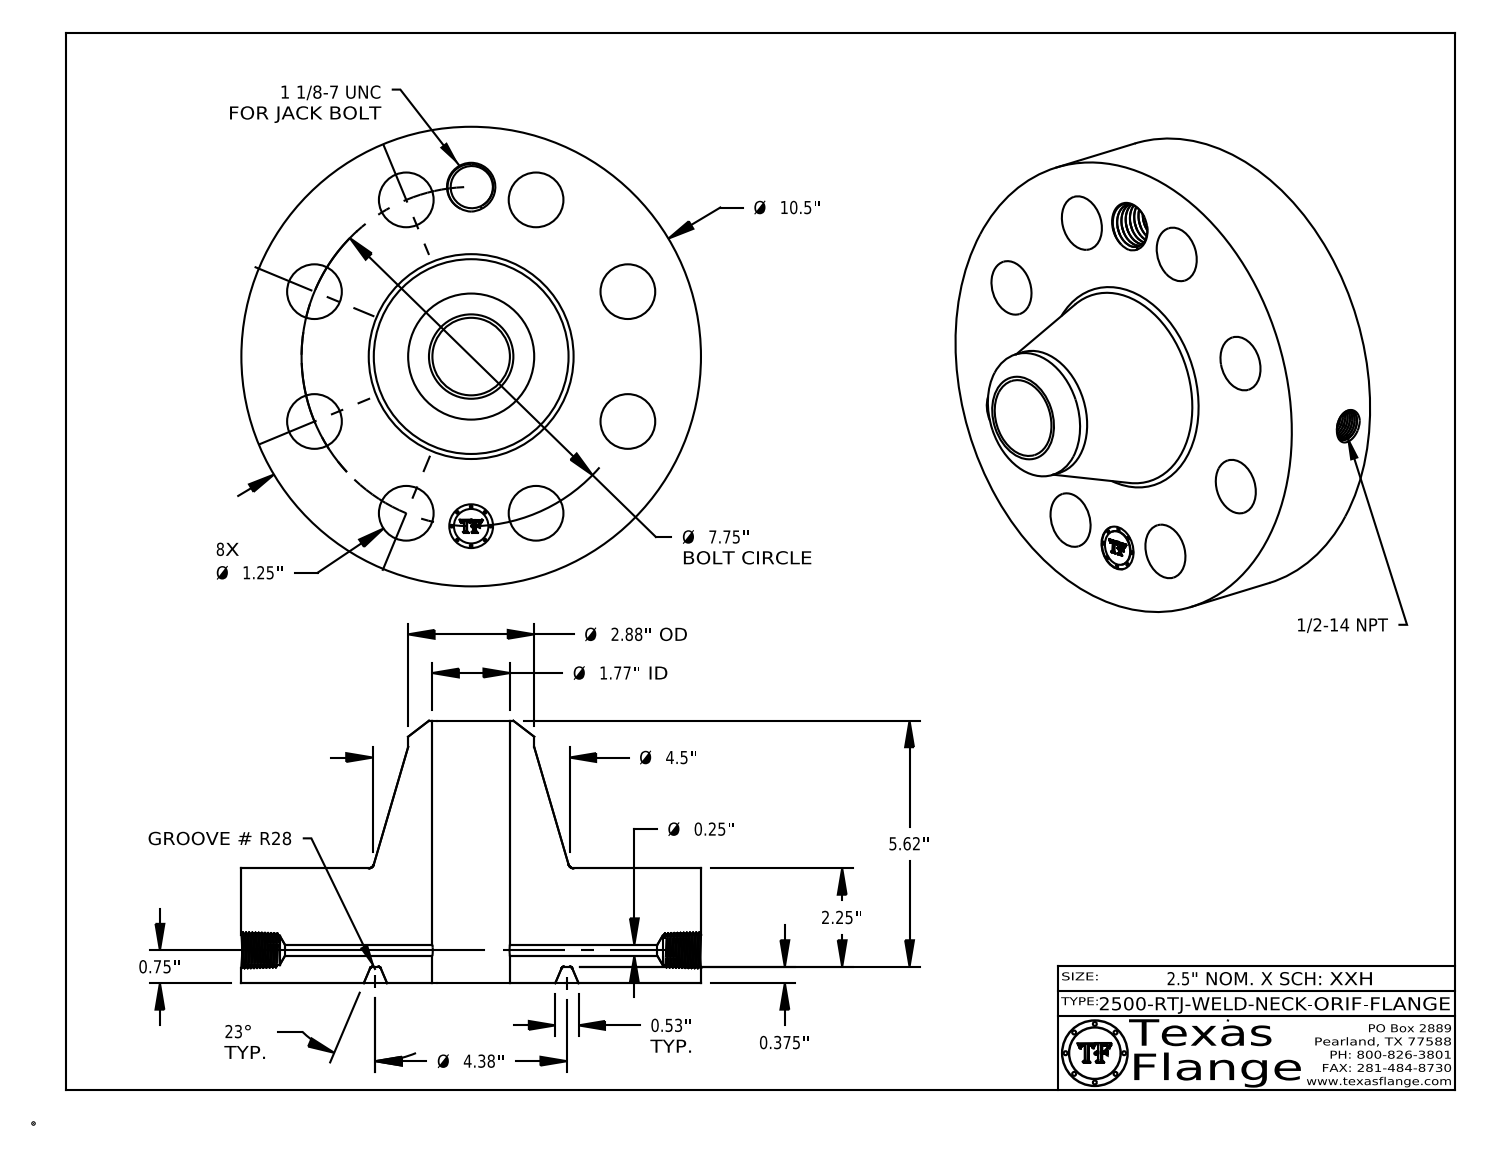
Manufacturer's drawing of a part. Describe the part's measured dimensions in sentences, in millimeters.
The part is named "2500-RTJ-WELD-NECK". Its 3-D file was written by "CATIA V5 STEP AP214 (AUTOMOTIVE_DESIGN)". It is 1 solid with 797 faces: 370 planar, 98 cylindrical and 329 other. Overall it measures 266.7 by 266.7 by 152.3 millimeters. Its volume is 3 520 000 cubic millimeters and its surface area 262 600 square millimeters. Round holes: 8 of diameter 31.8, 1 of diameter 6.4, 1 of diameter 17.1, 1 of diameter 25, 1 of diameter 25.4, 1 of diameter 45. Round bosses or shafts: 8 of diameter 1.5, 1 of diameter 266.7, 1 of diameter 73.2, 1 of diameter 20. The main face-to-face distances are 66.7, 9.5, 57.2, 152.3, 142.7, 85.6, 66.3, 56.8, 0.4, 86. The hole center spacings are 98.4, 139.2, 38.4, 75.3, 75.3, 109.4, 163.7, 181.9.
